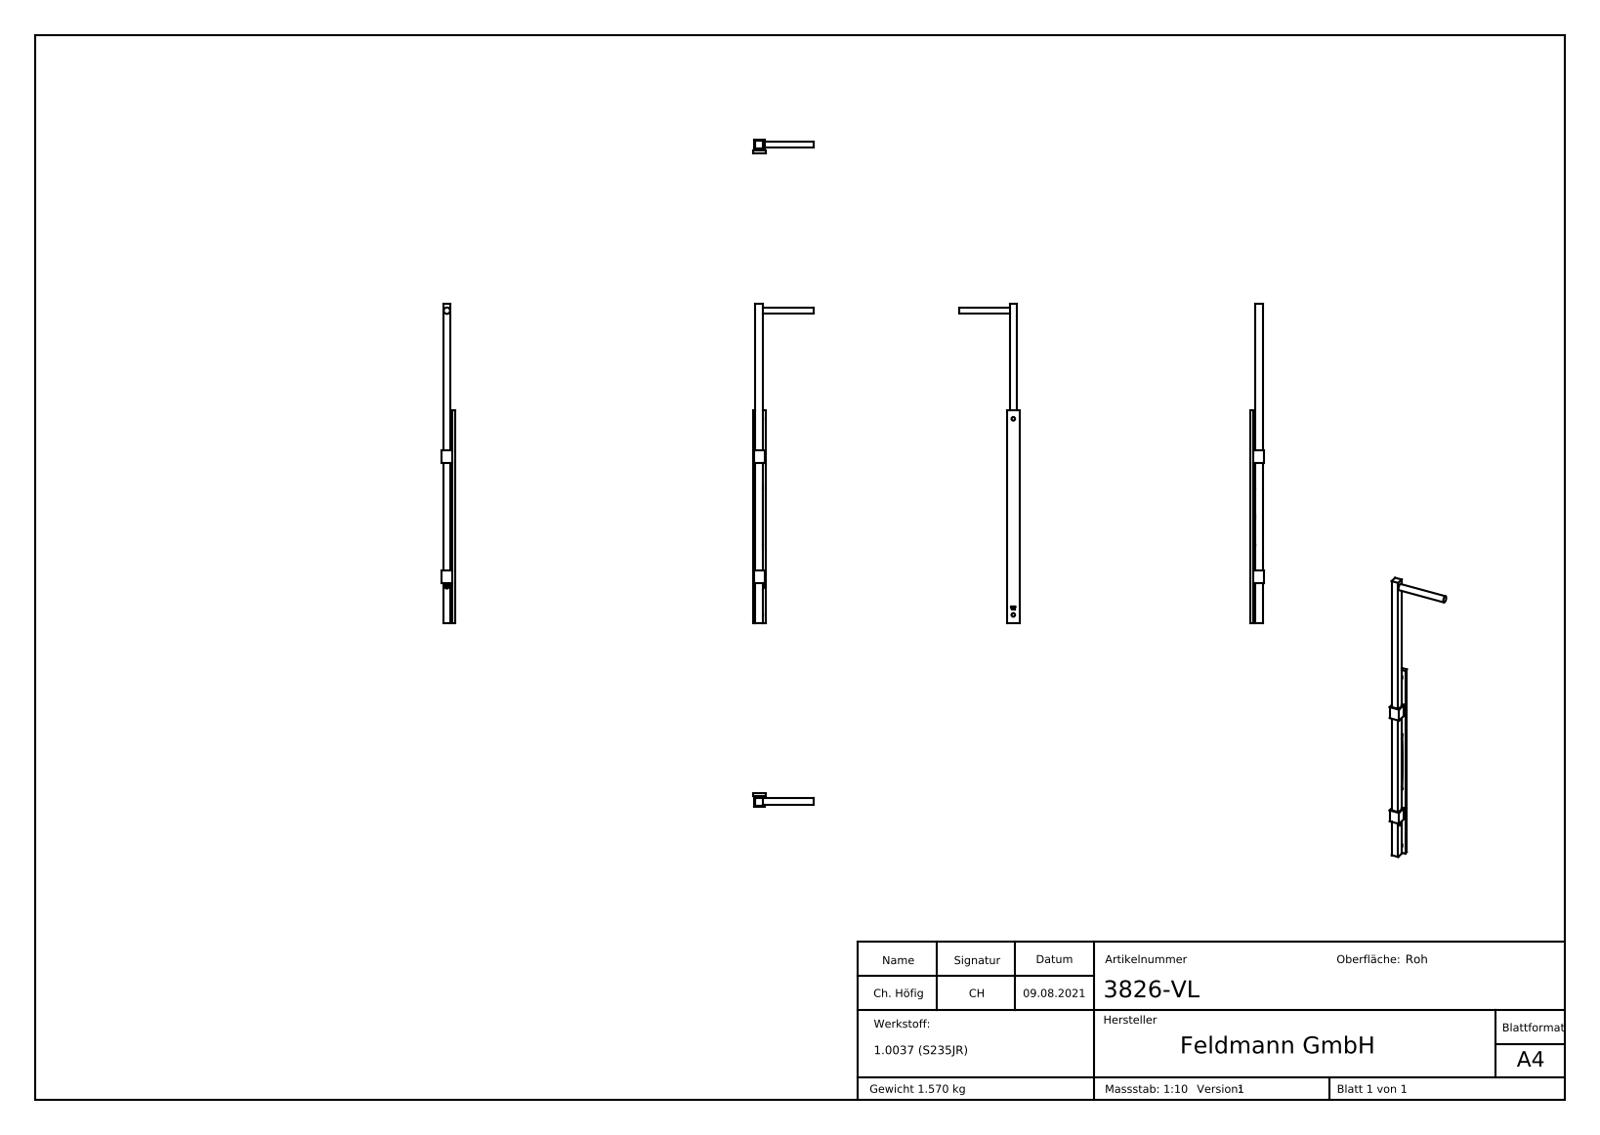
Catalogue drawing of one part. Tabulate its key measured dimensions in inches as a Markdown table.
| quantity | value |
| --- | --- |
| part name | 3826-VL |
| STEP written by | SolidWorks 2018 (CONFIG_CONTROL_DESIGN) |
| units | inches |
| bodies | 6 solids, 251 faces (144 planar, 10 cylindrical, 97 other) |
| overall size | 23.622 × 4.495 × 1.043 |
| volume | 12.28 in³ |
| surface area | 115.5 in² |
| round holes (diameter × count) | 0.266 × 2 |
| round bosses / shafts (diameter × count) | 0.472 × 1, 0.276 × 1 |
| partial cylindrical surfaces (radius × count) | 0.27 × 1, 0.341 × 1, 0.35 × 1, 0.381 × 1, 27.692 × 1, 27.731 × 1 |
| main face-to-face distances | 0.551, 0.256, 0.669, 0.118, 0.925, 0.374, 0.079, 0.709, 0.204, 0.755 |
| hole center spacings | 14.488 |
